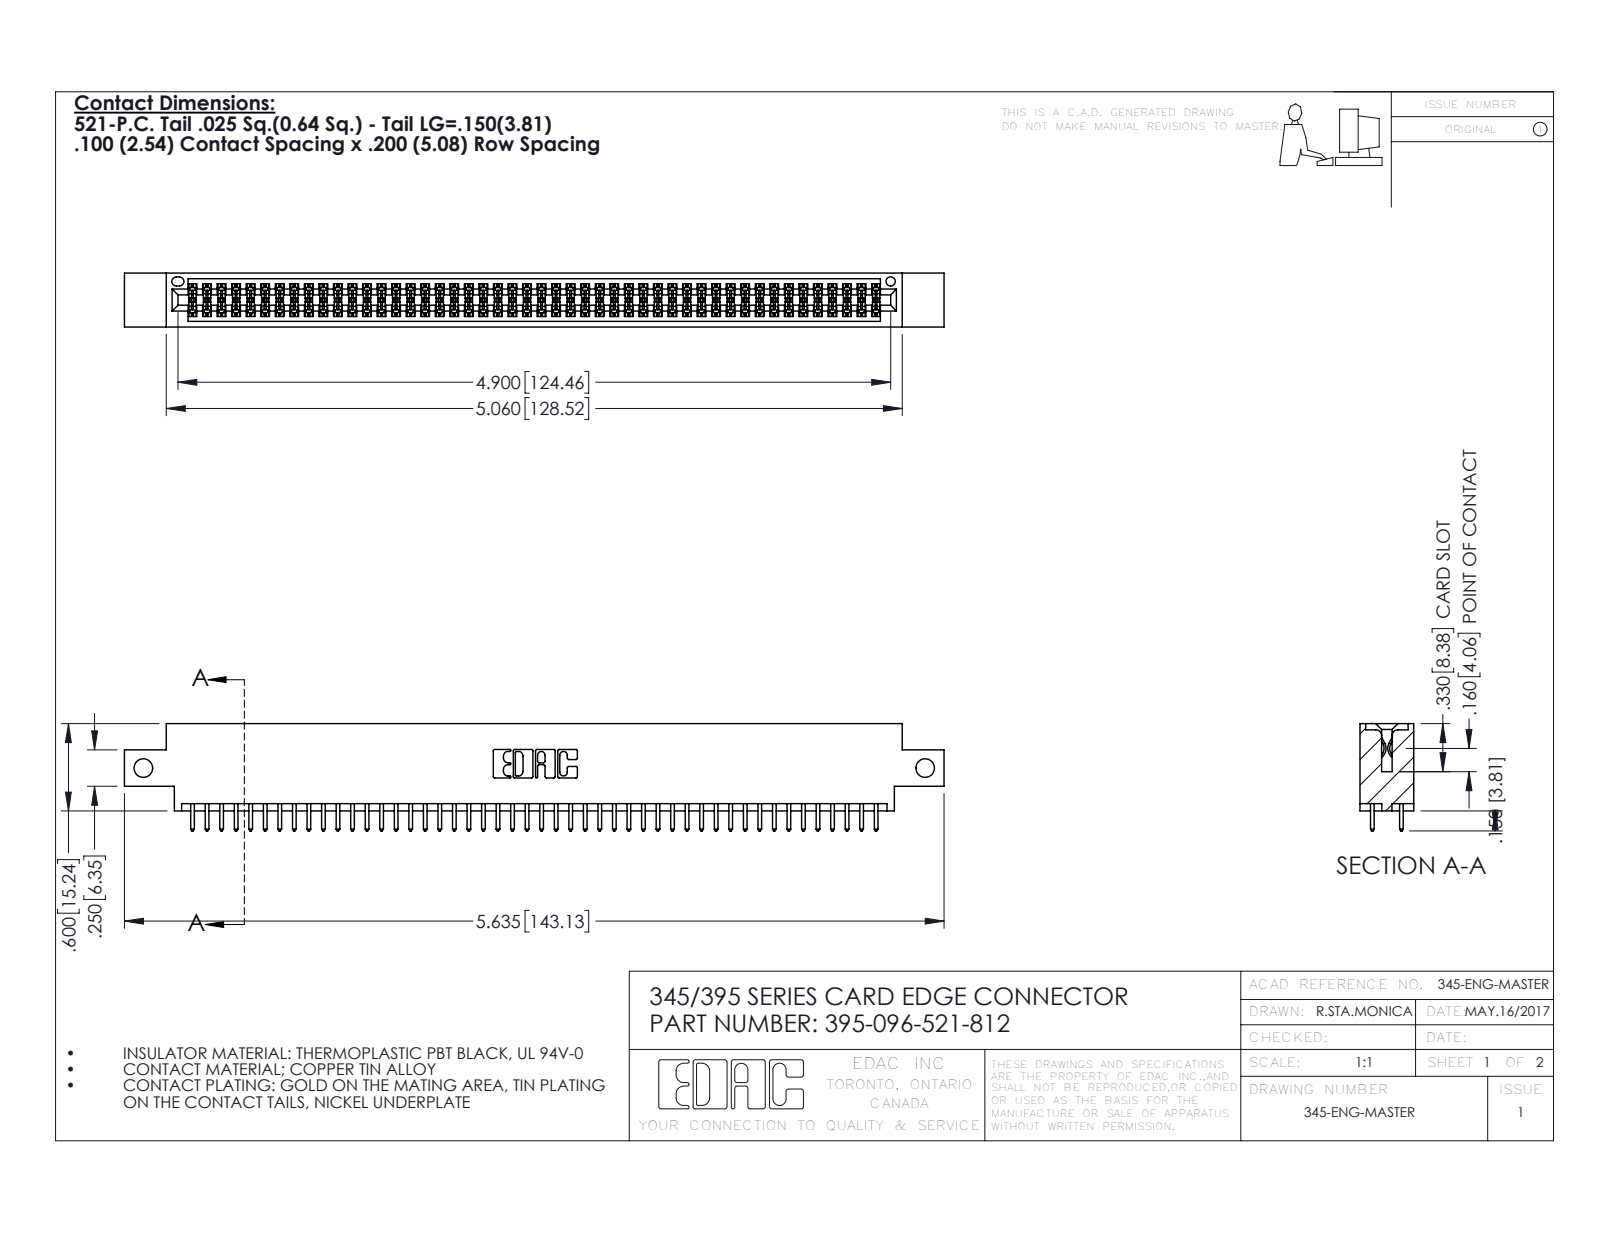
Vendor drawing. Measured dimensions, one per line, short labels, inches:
name: 345 Part_0.170 Offset - Side Mount; 345-292-001_345-293-121; 395-096-521-812
written by: SolidWorks 2016 (CONFIG_CONTROL_DESIGN)
unit: in
bodies: 97 solids, 4930 faces (3252 planar, 1678 cylindrical, 0 other)
size: 5.635 × 0.737 × 0.37
volume: 0.837 in³; area: 31.23 in²
holes: 2× ⌀0.128, 1× ⌀0.064
rounds: 144× R0.006, 96× R0.01, 22× R0.01, 6× R0.007, 6× R0.031, 3× R0.026, 2× R0.014, 2× R0.019
face distances: 0.072, 0.298, 0.37, 0.2, 0.098, 0.272, 0.025, 0.225, 0.175, 0.149
hole spacings: 5.375
